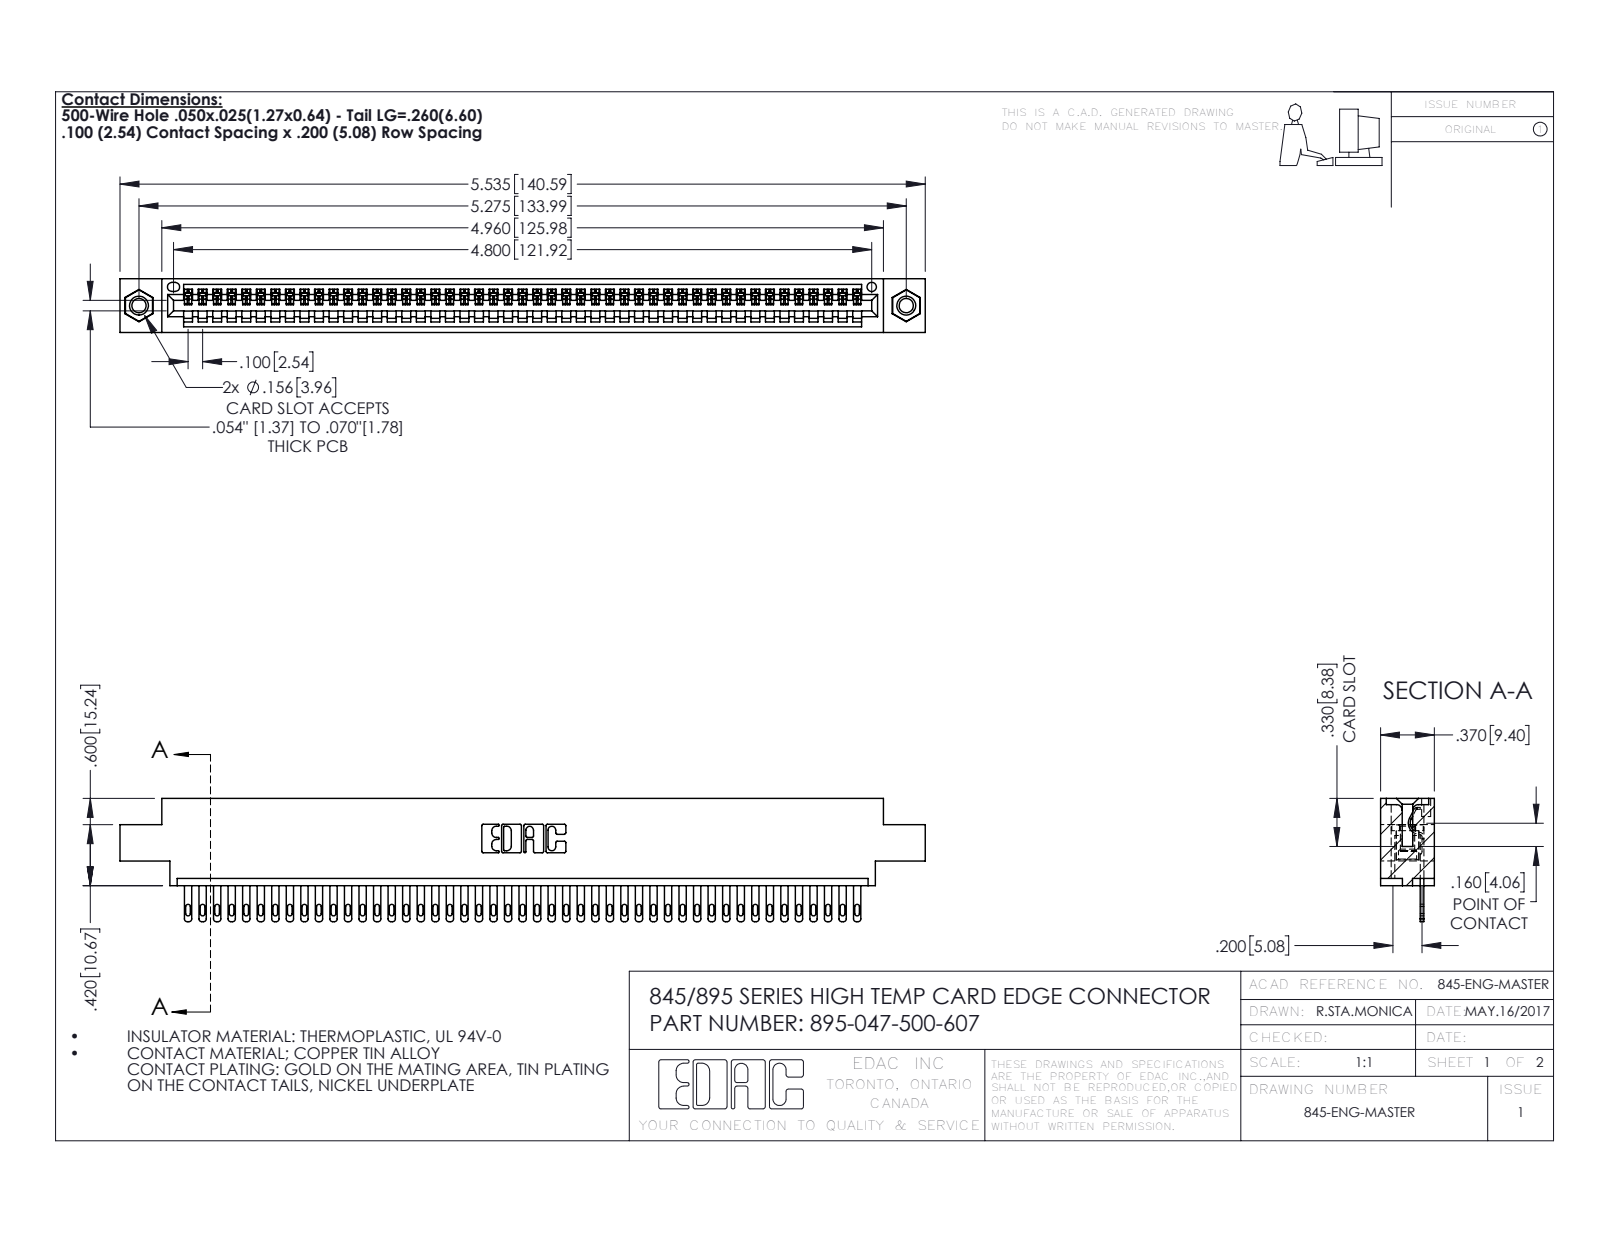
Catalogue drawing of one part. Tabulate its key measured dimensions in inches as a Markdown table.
| quantity | value |
| --- | --- |
| part name | 345-292-001_345-293-100; 345-250-001_345-250-005-103; 845 Part_0.170 Offset - 0.156 Dia-TI; 895-047-500-607 |
| STEP written by | SolidWorks 2020 (CONFIG_CONTROL_DESIGN) |
| units | inches |
| bodies | 50 solids, 2728 faces (1714 planar, 998 cylindrical, 16 other) |
| overall size | 5.535 × 0.847 × 0.37 |
| volume | 0.811 in³ |
| surface area | 27.9 in² |
| round holes (diameter × count) | 0.098 × 2, 0.125 × 2, 0.156 × 2, 0.064 × 1 |
| round bosses / shafts (diameter × count) | 0.155 × 2 |
| partial cylindrical surfaces (radius × count) | 0.006 × 94, 0.016 × 94, 0.02 × 94, 0.01 × 22, 0.007 × 6, 0.031 × 6, 0.026 × 3, 0.031 × 2 |
| main face-to-face distances | 0.072, 0.298, 0.37, 0.098, 0.272, 0.025, 0.2, 0.225, 0.175, 0.149 |
| hole center spacings | 0.27, 5.039, 5.275 |
